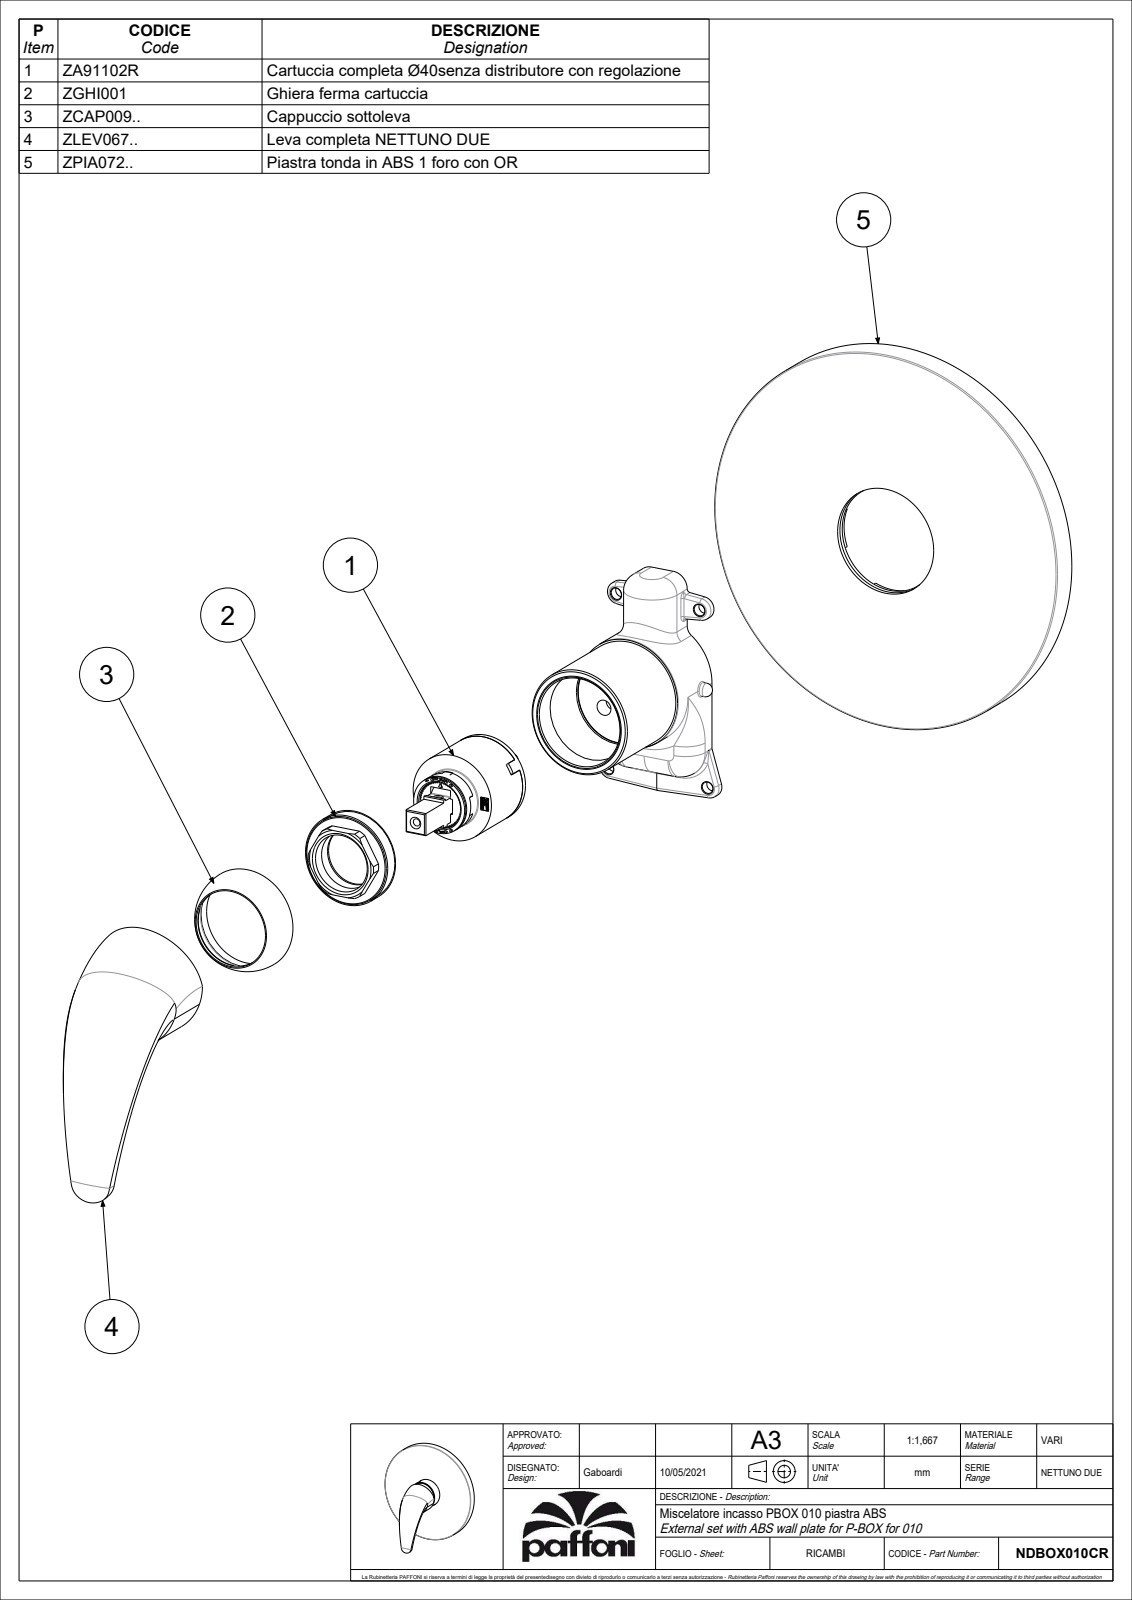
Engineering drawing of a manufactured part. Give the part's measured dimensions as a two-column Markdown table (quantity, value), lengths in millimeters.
| quantity | value |
| --- | --- |
| part name | NDBOX010CR |
| STEP written by | CREO PARAMETRIC BY PTC INC, 2020044 (CONFIG_CONTROL_DESIGN) |
| units | millimeters |
| bodies | 1 solid, 66 faces (29 planar, 12 cylindrical, 25 other) |
| overall size | 174.82 × 173 × 89.7 |
| volume | 400 773 mm³ |
| surface area | 73 085 mm² |
| round holes (diameter × count) | 6 × 1 |
| round bosses / shafts (diameter × count) | 173 × 1, 48.1 × 1 |
| partial cylindrical surfaces (radius × count) | 3.9 × 1, 4 × 1 |
| main face-to-face distances | 13, 45.7, 32.7, 59.95, 46.95, 14.25, 15.3, 18.1, 11, 3.5 |
